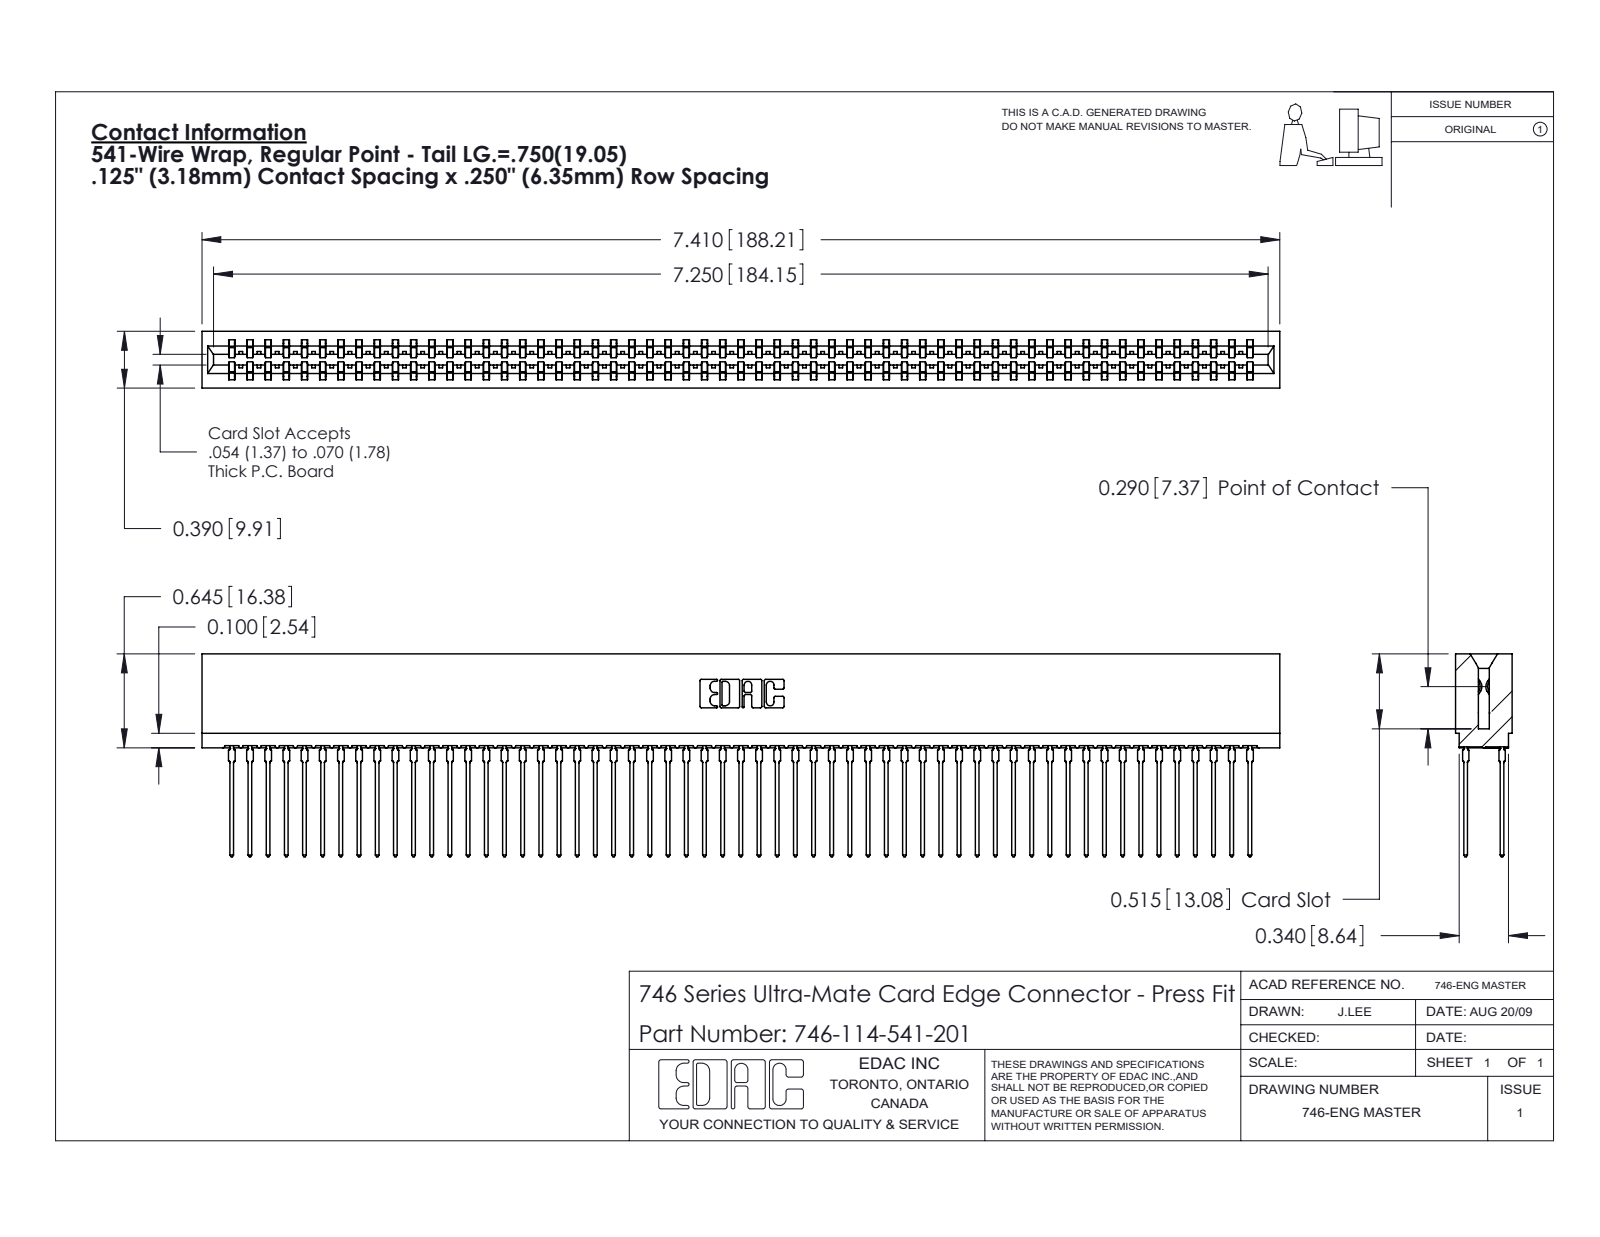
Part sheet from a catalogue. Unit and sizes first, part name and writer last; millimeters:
Units: millimetres
Overall size (bounding box): 188.2 × 35.4 × 9.9
Partial cylindrical surfaces — rounded edges, fillets, slot ends (radius × count): R0.5 ×228, R0.4 ×58, R0.3 ×22, R0.1 ×8, R0.3 ×8, R0.2 ×6, R0.8 ×6, R0.7 ×3
Main face-to-face distances: 1.4, 8.5, 6.4, 0.6, 7.8, 9.9, 2.1, 7, 4.4, 4
Volume: 20 700 mm³ · Surface area: 36 470 mm²
Bodies: 115 solids, 10300 faces (5299 planar, 2037 cylindrical, 2964 other)
Part name (STEP PRODUCT): 746-292-001_541; 746 Part_.515 Slot Depth - 01; 746-114-541-201
STEP written by: SolidWorks 2020 (CONFIG_CONTROL_DESIGN)
